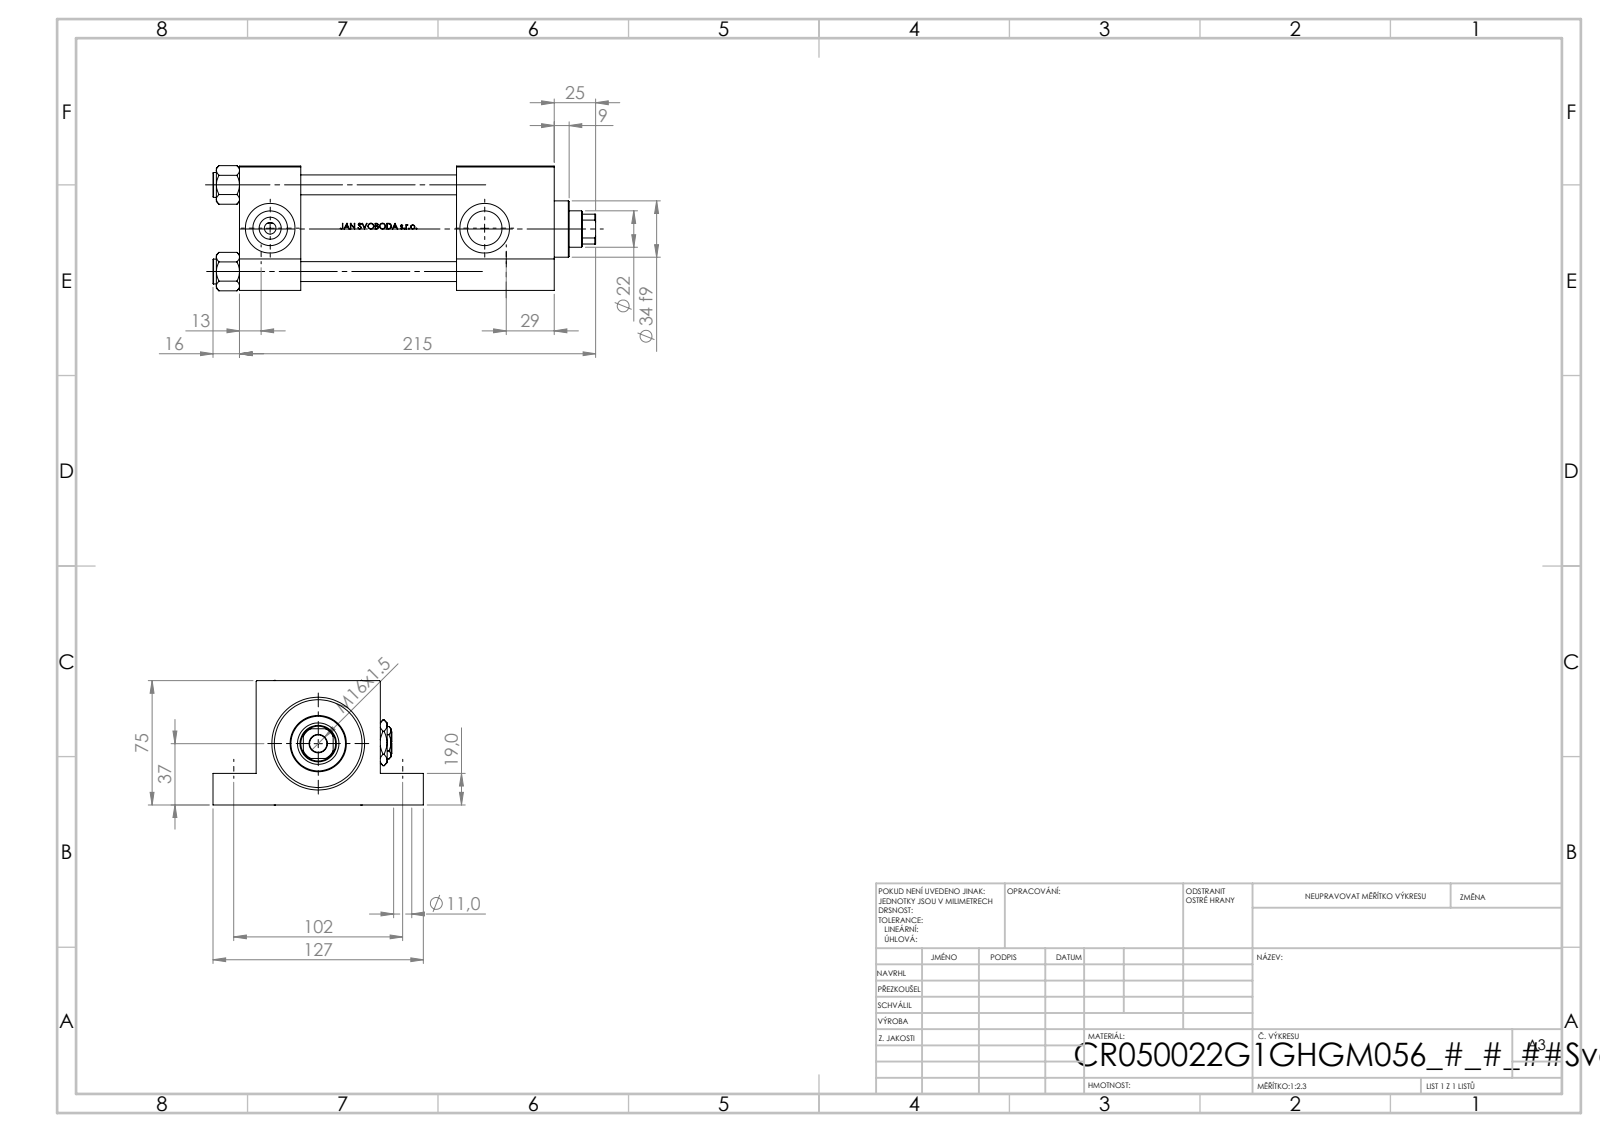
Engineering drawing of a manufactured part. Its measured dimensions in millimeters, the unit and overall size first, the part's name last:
Units: millimetres
Overall size (bounding box): 231 × 127 × 75.54
Round holes (diameter × count): ⌀11 ×4, ⌀12 ×4, ⌀7 ×2, ⌀20.96 ×2, ⌀30 ×2, ⌀10.5 ×1, ⌀22 ×1, ⌀25 ×1, ⌀41 ×1, ⌀50 ×1, ⌀53 ×1
Round bosses / shafts (diameter × count): ⌀15 ×4, ⌀56 ×1, ⌀34 ×1
Partial cylindrical surfaces — rounded edges, fillets, slot ends (radius × count): R10.5 ×1
Main face-to-face distances: 75, 37, 56, 190, 153, 19, 131, 94, 59, 26
Hole centre spacings: 52.3, 36.63, 37.34, 73.96, 102, 148, 179.74, 129.5
Volume: 800 388 mm³ · Surface area: 181 179 mm²
Bodies: 12 solids, 1134 faces (454 planar, 128 cylindrical, 552 other)
Part name (STEP PRODUCT): V215CR_G_TYCINKA; V215CR_G_Body; V215CR_VCP_G; NUT_M5_G (+2 more)
STEP written by: SolidWorks 2019 (CONFIG_CONTROL_DESIGN)
